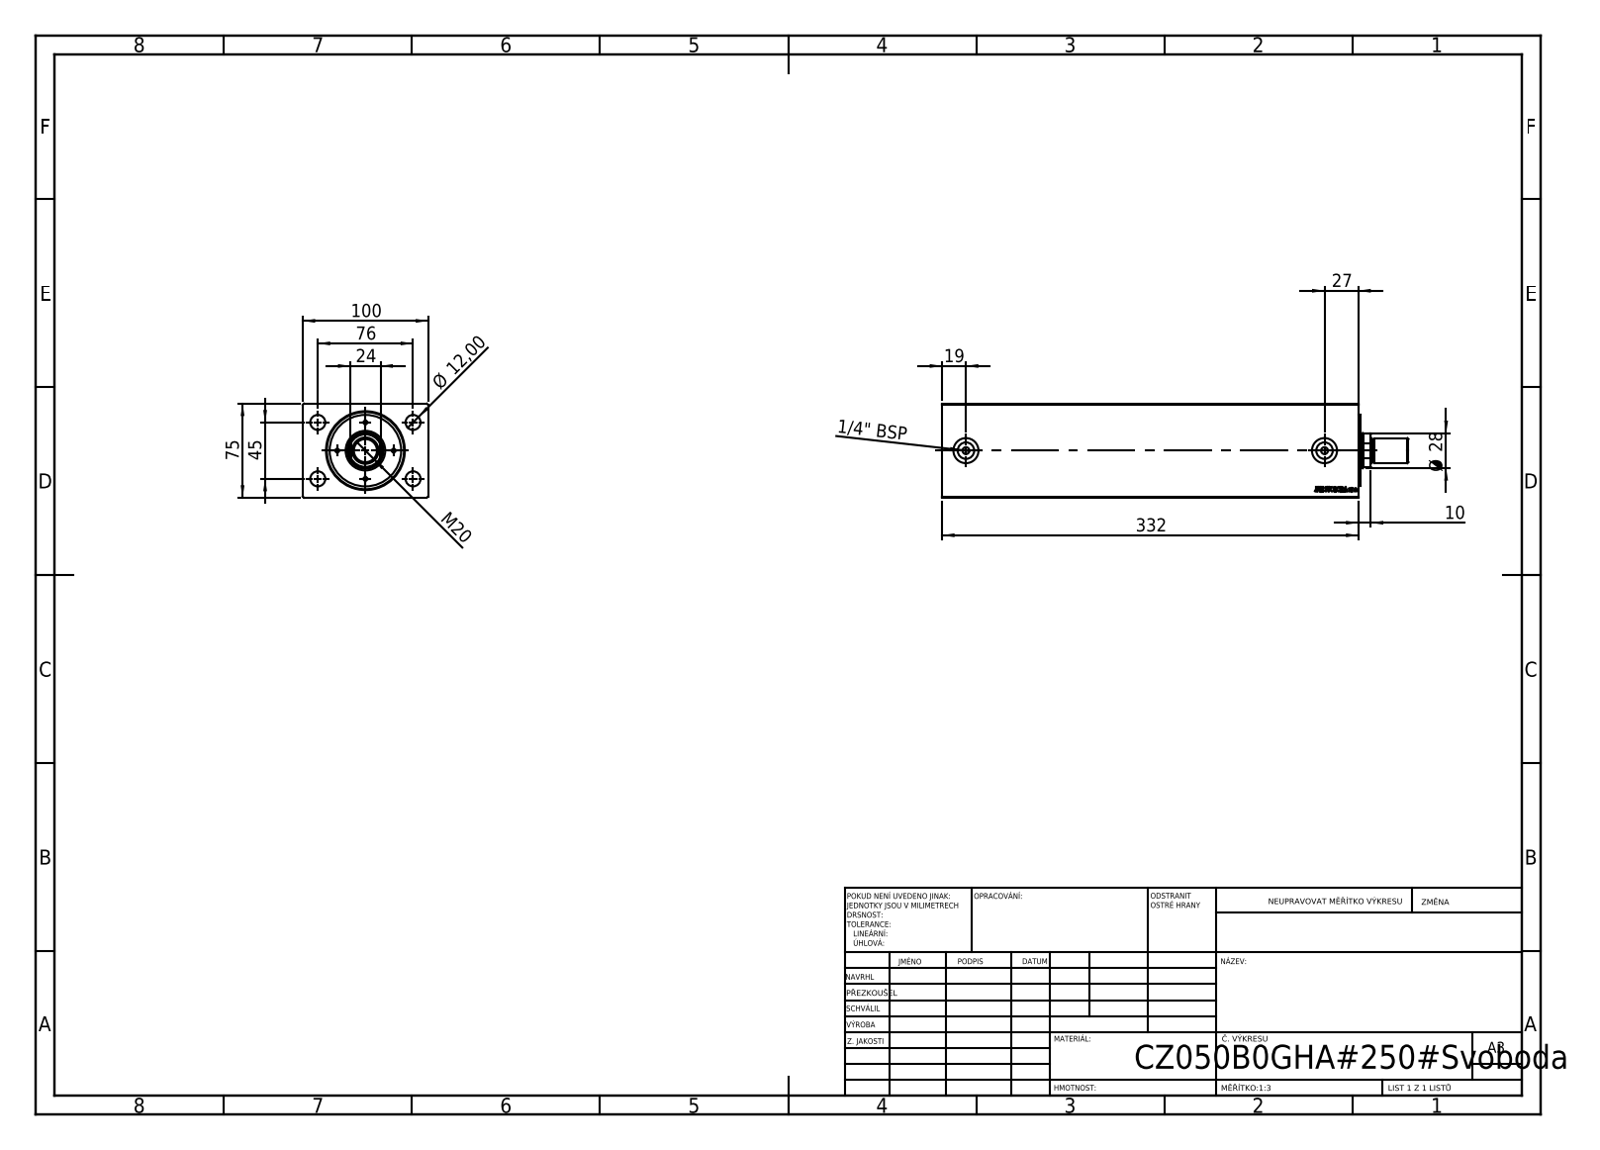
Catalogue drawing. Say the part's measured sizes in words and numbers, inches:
The part is named "V500CZ_B_VC; V500CZ; V500CZ_MALE_METRIC". Its 3-D file was written by "SolidWorks 2019 (CONFIG_CONTROL_DESIGN)". It is 4 solids with 888 faces: 404 planar, 62 cylindrical and 422 other. Overall it measures 14.646 by 3.937 by 2.953 inches. Its volume is 130 cubic inches and its surface area 367.3 square inches. Round holes: 4 of diameter 0.118, 4 of diameter 0.472, 2 of diameter 0.217, 2 of diameter 0.518, 2 of diameter 0.787, 1 of diameter 0.728, 1 of diameter 1.102, 1 of diameter 1.142, 1 of diameter 1.417, 1 of diameter 1.969, 1 of diameter 2.421. Round bosses or shafts: 1 of diameter 2.244, 1 of diameter 0.787, 1 of diameter 0.709. Partial cylindrical surfaces (rounded edges, fillets, slot ends): 1 of radius 0.531. The main face-to-face distances are 2.953, 3.937, 13.071, 12.37, 0.701, 0.394, 0.323, 0.071, 12.047, 12.748. The hole center spacings are 0.886, 1.076, 1.253, 1.496, 1.739, 1.772, 2.319, 2.541.
